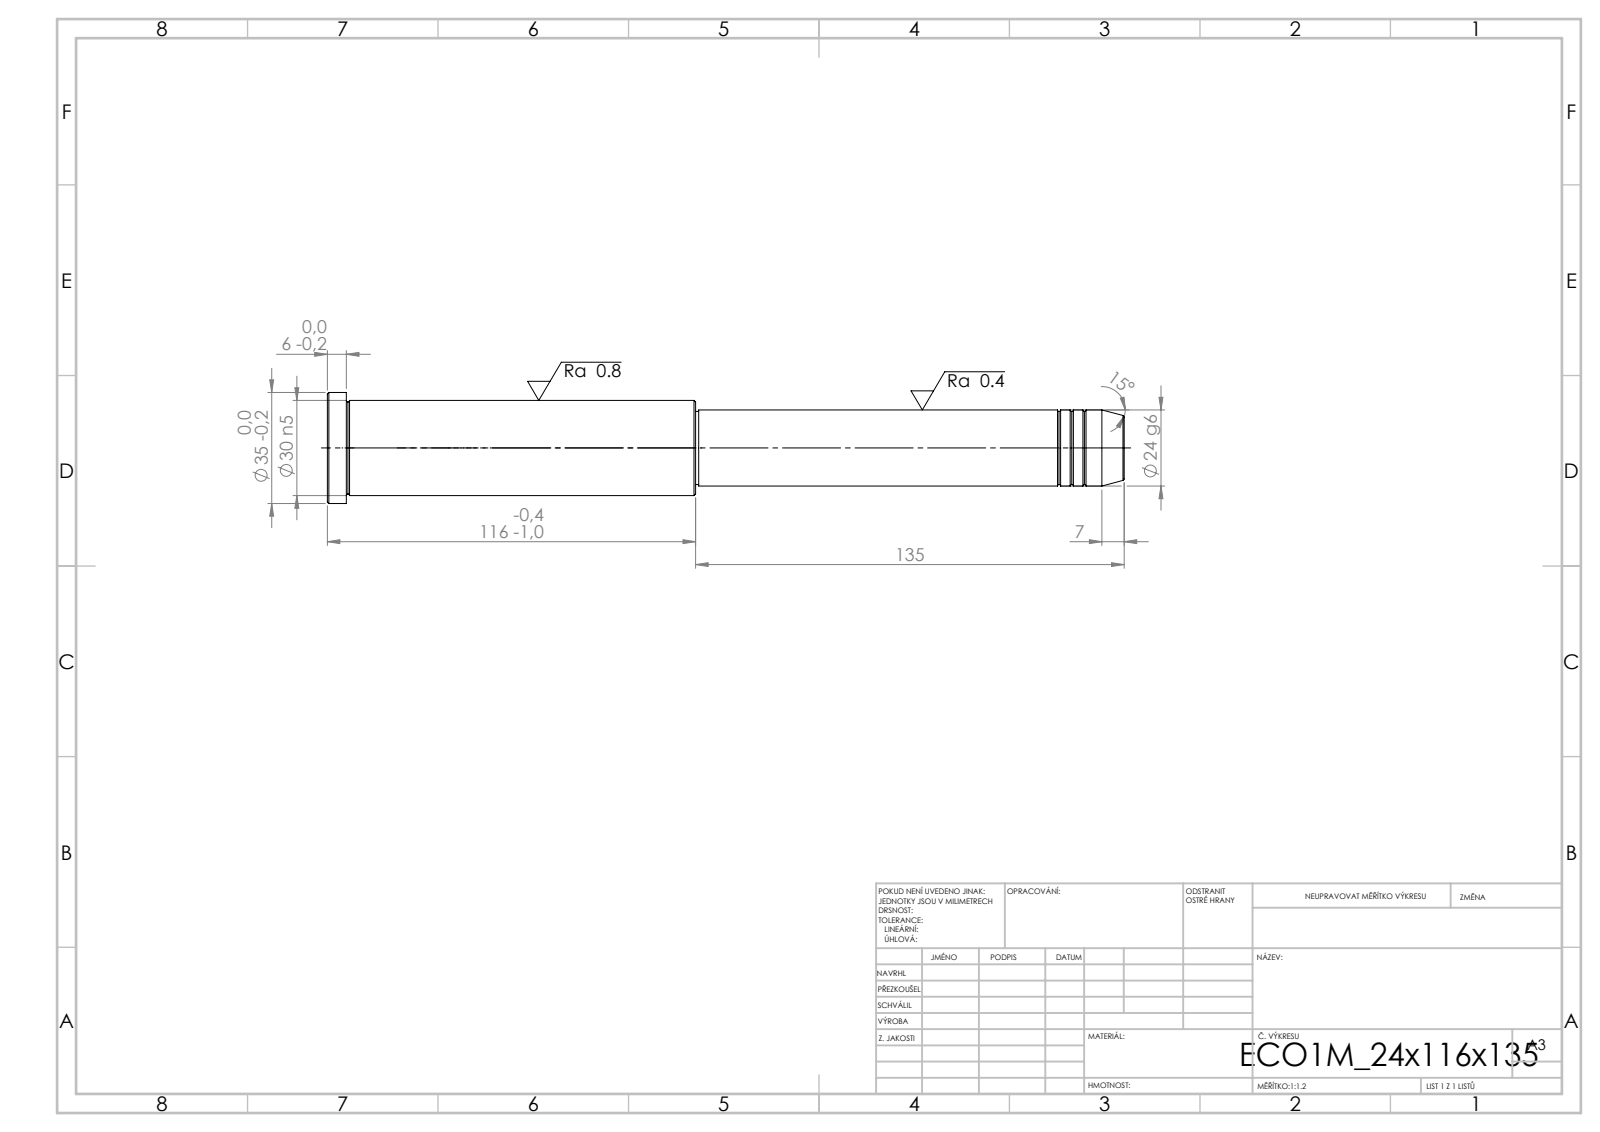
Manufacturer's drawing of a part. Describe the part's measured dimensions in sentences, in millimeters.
Its 3-D file was written by "SolidWorks 2019 (CONFIG_CONTROL_DESIGN)". It is 1 solid with 43 faces: 5 planar, 14 cylindrical and 24 other. Overall it measures 251 by 35 by 35 millimeters. Its volume is 143 943 cubic millimeters and its surface area 23 149 square millimeters. Round bosses or shafts: 1 of diameter 35, 1 of diameter 30, 1 of diameter 24, 1 of diameter 23. The main face-to-face distances are 251, 245, 6, 135, 110, 116, 134, 1, 111, 117.
